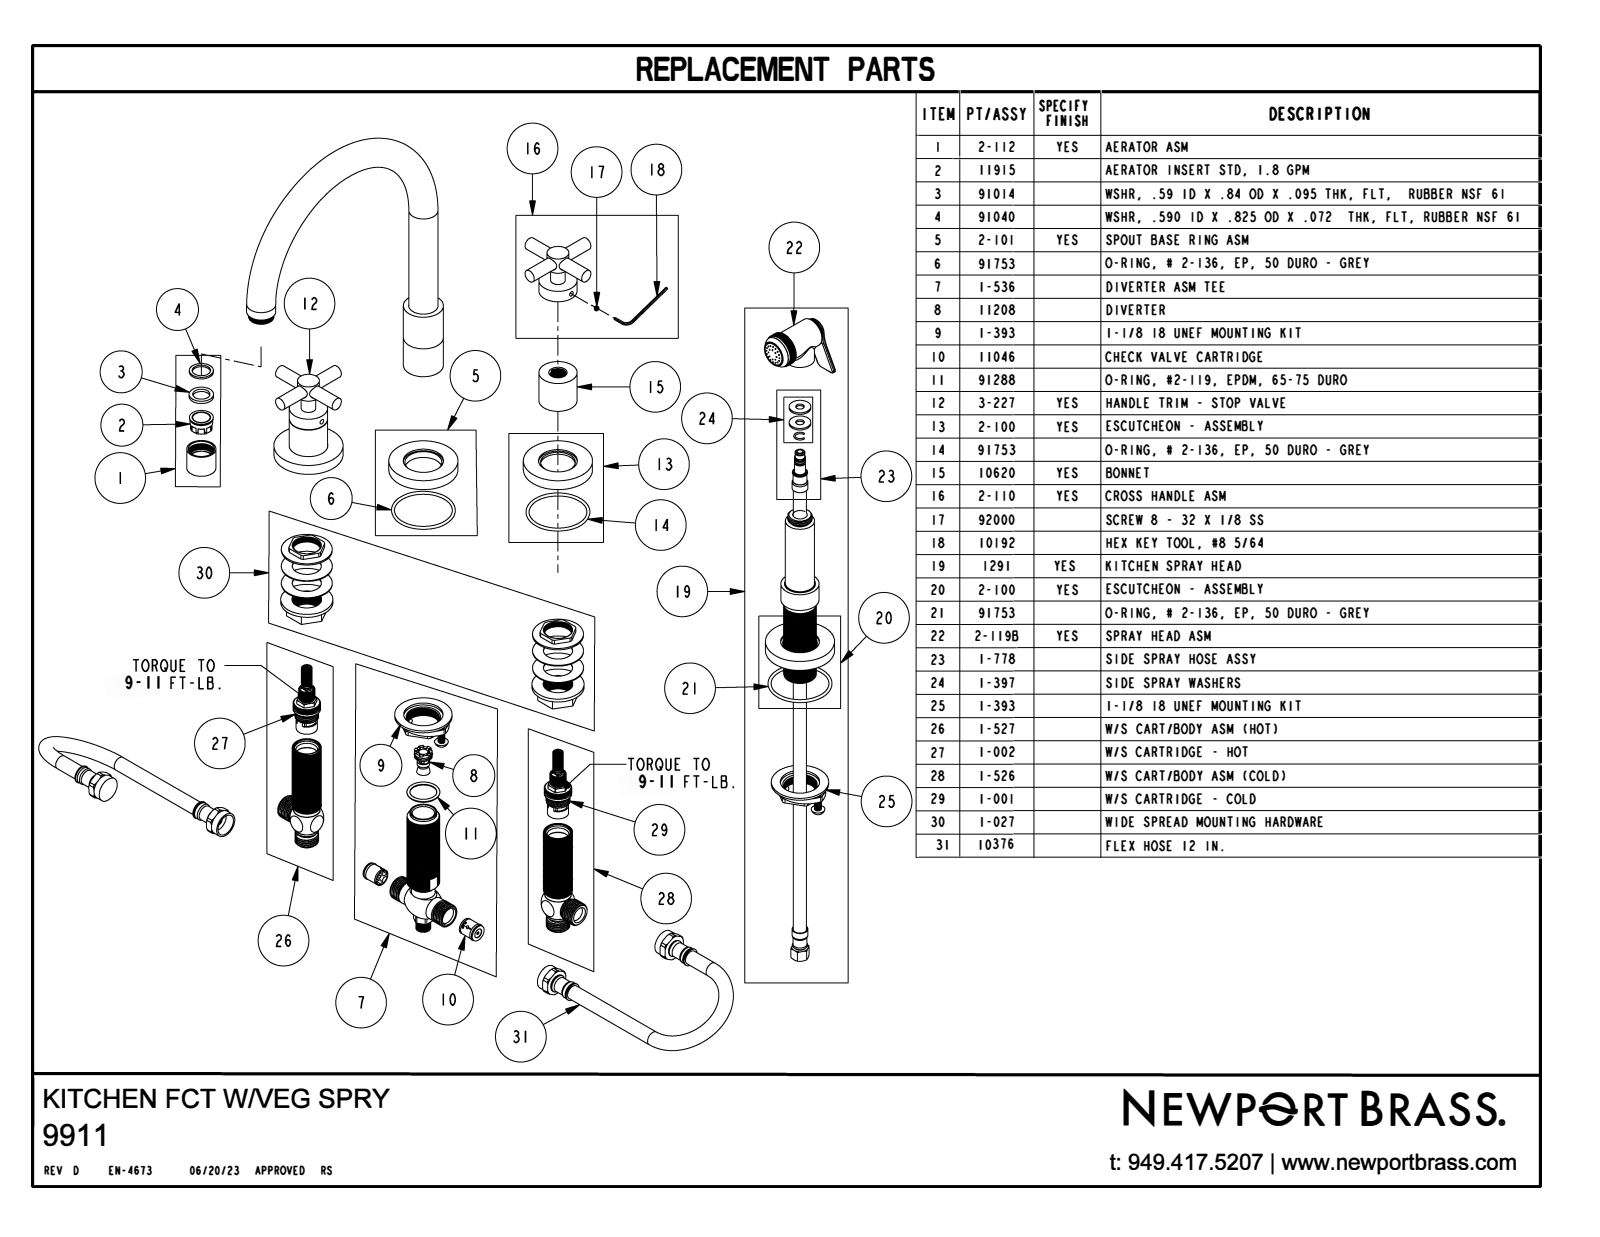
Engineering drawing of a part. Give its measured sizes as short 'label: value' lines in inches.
name: 9911
written by: CREO PARAMETRIC BY PTC INC, 2018400 (AUTOMOTIVE_DESIGN)
unit: in
bodies: 6 solids, 612 faces (301 planar, 221 cylindrical, 90 other)
size: 16.563 × 11.248 × 9.765
volume: 35.21 in³; area: 178.7 in²
holes: 1× ⌀0.06, 1× ⌀0.231, 1× ⌀0.968, 1× ⌀1.005
bosses: 4× ⌀2.375, 3× ⌀1, 3× ⌀0.445, 2× ⌀1.313, 2× ⌀0.75, 2× ⌀0.5, 1× ⌀1.375, 1× ⌀1.313
rounds: 10× R0.04, 5× R0.07, 4× R0.06, 2× R0.156, 2× R0.16, 1× R0.332, 1× R0.34, 1× R0.385
face distances: 0.375, 0.02, 1.483, 1.503, 1.108, 1.128, 1.943, 1.568, 0.46, 0.44
